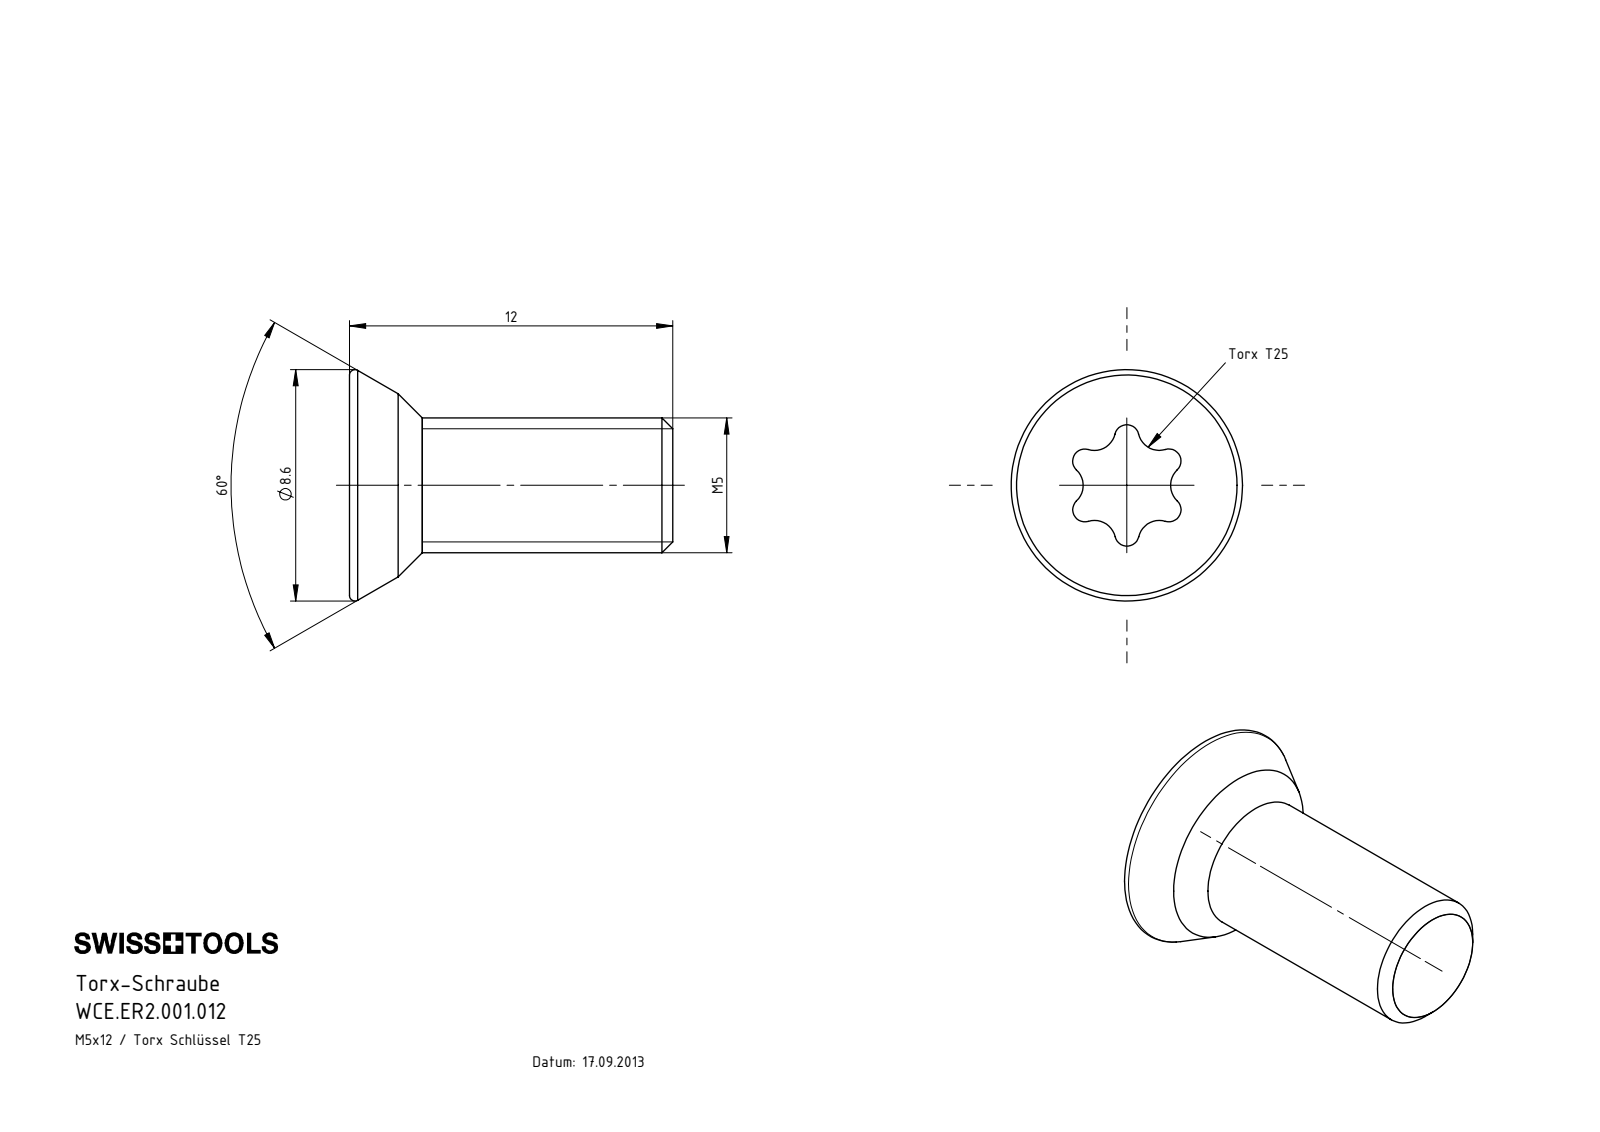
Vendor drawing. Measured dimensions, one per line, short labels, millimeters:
name: WCE.ER2.001.012
written by: SolidWorks 2017 (AUTOMOTIVE_DESIGN)
unit: mm
bodies: 1 solid, 28 faces (3 planar, 17 cylindrical, 8 other)
size: 12 × 8.59 × 8.59
volume: 275 mm³; area: 313 mm²
bosses: 1× ⌀5
rounds: 6× R0.45, 4× R0.79, 2× R0.79
face distances: 12, 1.5, 10.5
